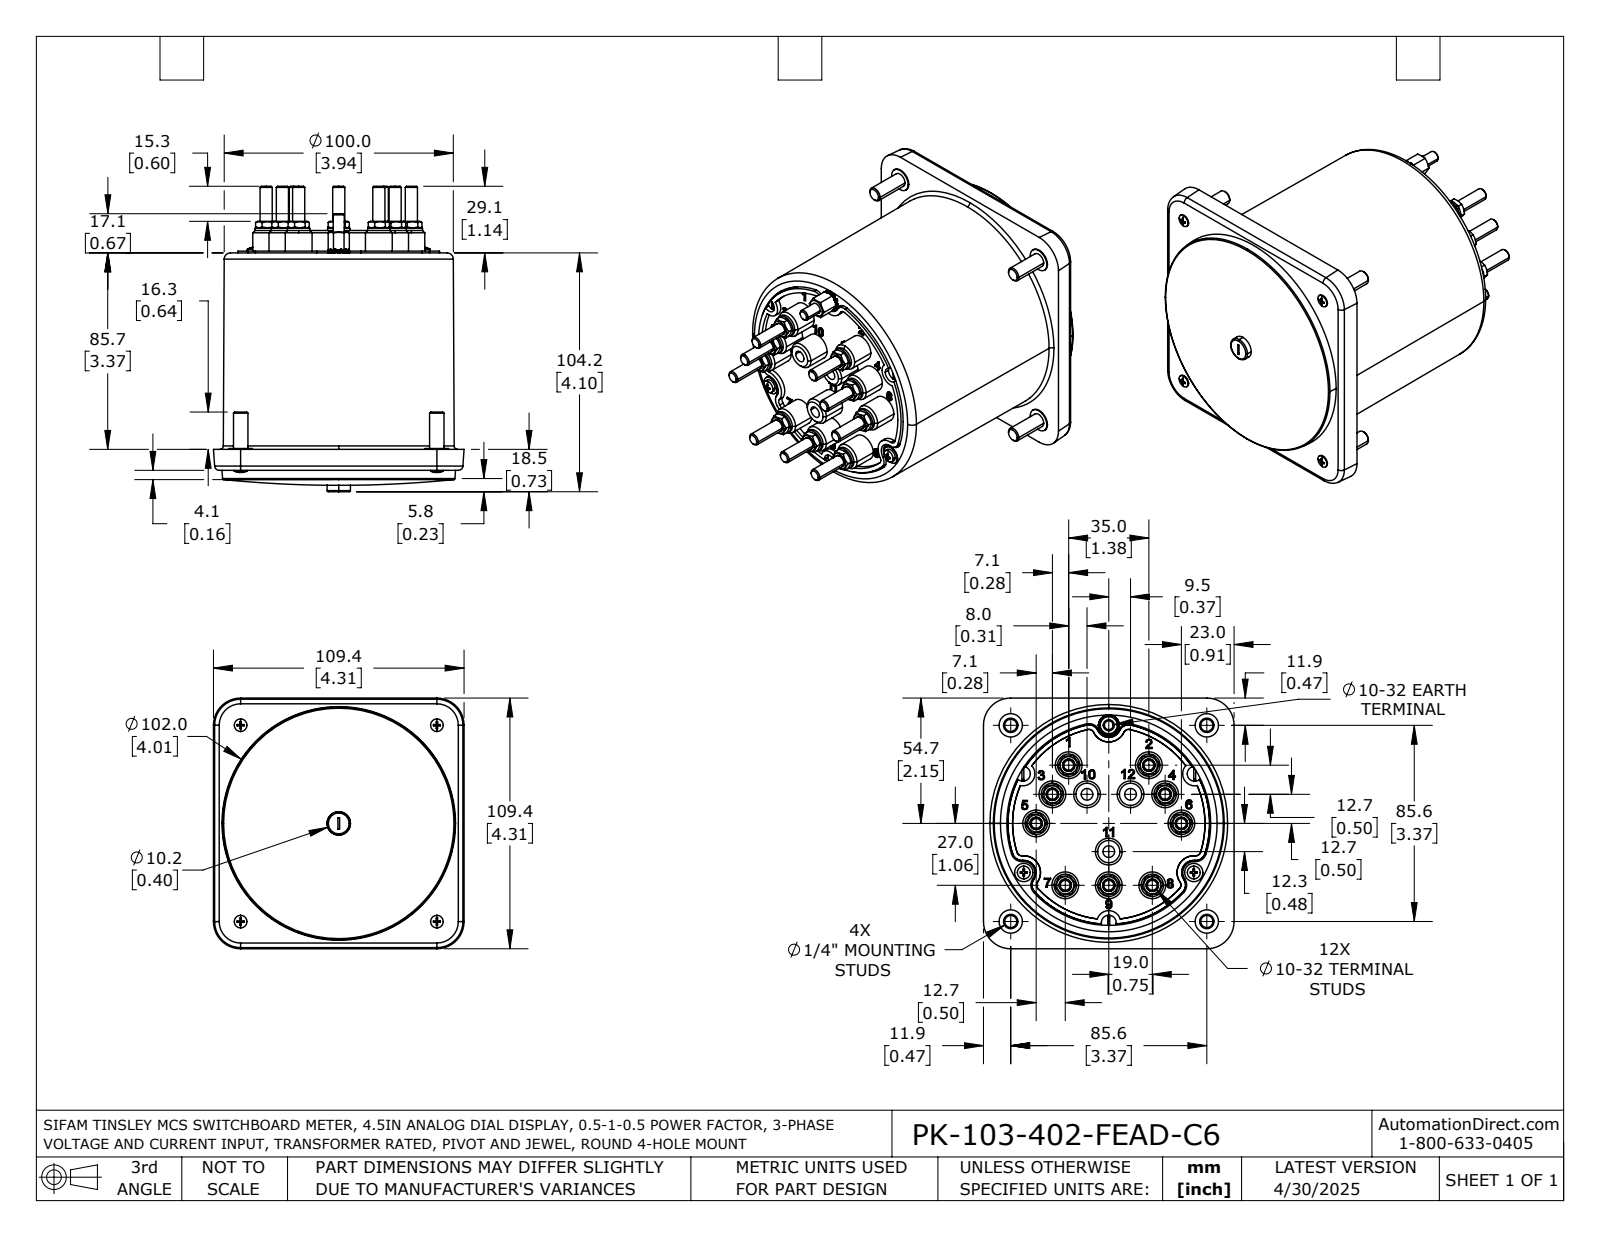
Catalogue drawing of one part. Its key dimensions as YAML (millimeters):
part_name: "PK-103-402-FEAD-C6"
step_written_by: "SolidWorks 2024 (AUTOMOTIVE_DESIGN)"
units: millimeters
bodies: {solids: 1, faces: 2018, planar: 623, cylindrical: 990, other: 405}
overall_size: [133.3, 109.4, 109.4]
volume: 841138
surface_area: 73728
round_holes:
  - {diameter: 2.4, count: 4}
  - {diameter: 3.9, count: 3}
  - {diameter: 4, count: 3}
  - {diameter: 4.65, count: 3}
  - {diameter: 5.1, count: 3}
  - {diameter: 6.1, count: 3}
  - {diameter: 6.5, count: 3}
  - {diameter: 4.5, count: 2}
  - {diameter: 3.5, count: 1}
  - {diameter: 4.55, count: 1}
round_bosses_or_shafts:
  - {diameter: 11.7, count: 12}
  - {diameter: 9.76, count: 9}
  - {diameter: 5.3, count: 9}
  - {diameter: 10.2, count: 4}
  - {diameter: 6.3, count: 4}
  - {diameter: 5.5, count: 4}
  - {diameter: 5.9, count: 3}
  - {diameter: 4.45, count: 3}
partial_cylinders:
  - {radius: 0.22, count: 286}
  - {radius: 1.08, count: 283}
  - {radius: 0.68, count: 12}
  - {radius: 4.5, count: 11}
  - {radius: 0.68, count: 10}
  - {radius: 4.8, count: 9}
  - {radius: 2, count: 4}
  - {radius: 5.25, count: 3}
face_to_face_distances: [84.5, 93.65, 9.15, 1.22, 85.72, 94.87, 0.78, 2, 86.5, 95.65]
hole_center_spacings: [43.07, 42.8, 43.08, 74.21, 85.6, 64.72, 74.22, 75]
